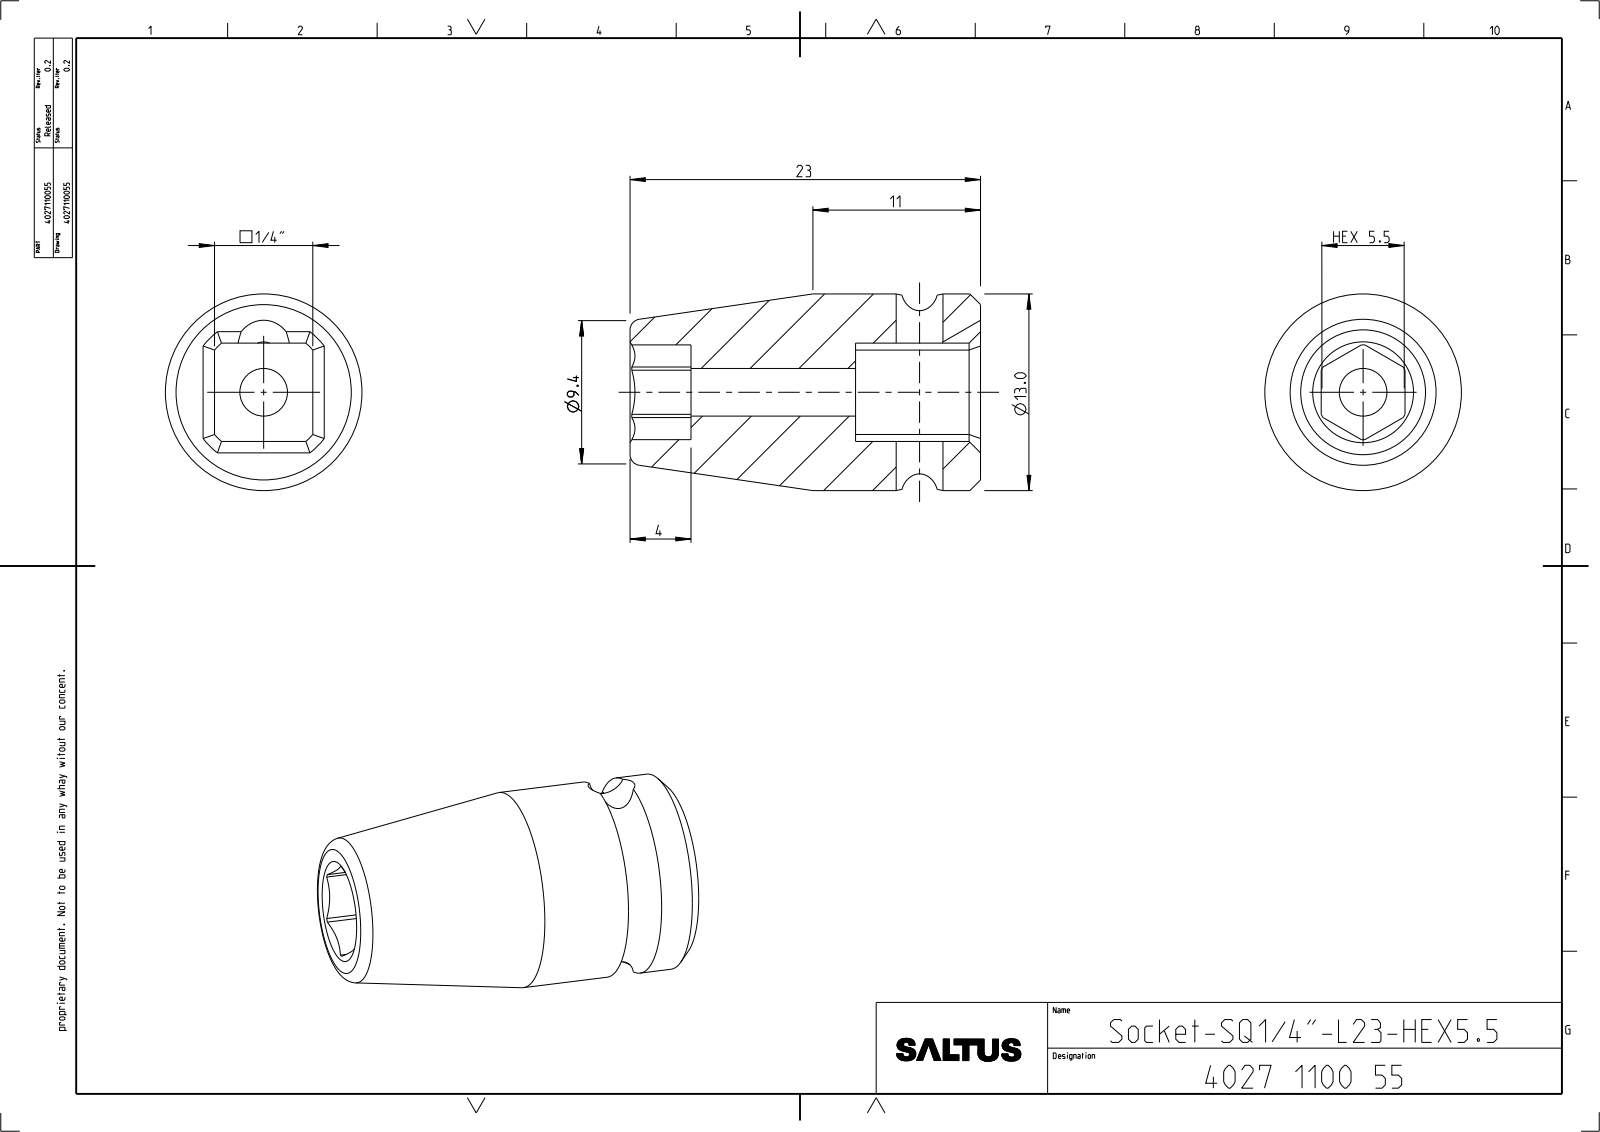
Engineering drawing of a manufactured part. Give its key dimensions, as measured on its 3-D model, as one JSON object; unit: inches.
{"part_name": "4027110055", "step_written_by": "CREO PARAMETRIC BY PTC INC, 2022414 (CONFIG_CONTROL_DESIGN)", "units": "inches", "bodies": {"solids": 1, "faces": 54, "planar": 19, "cylindrical": 21, "other": 14}, "overall_size": [0.906, 0.508, 0.508], "volume_in3": 0.12, "surface_area_in2": 2.238, "round_holes": [[0.121, 1], [0.123, 1]], "round_bosses_or_shafts": [[0.508, 1]], "partial_cylinders_radius": [[0.079, 1], [0.122, 1], [0.167, 1]], "face_to_face_distances": [0.254, 0.323, 0.217, 0.019, 0.235, 0.748, 0.425, 0.906, 0.583, 0.157]}
